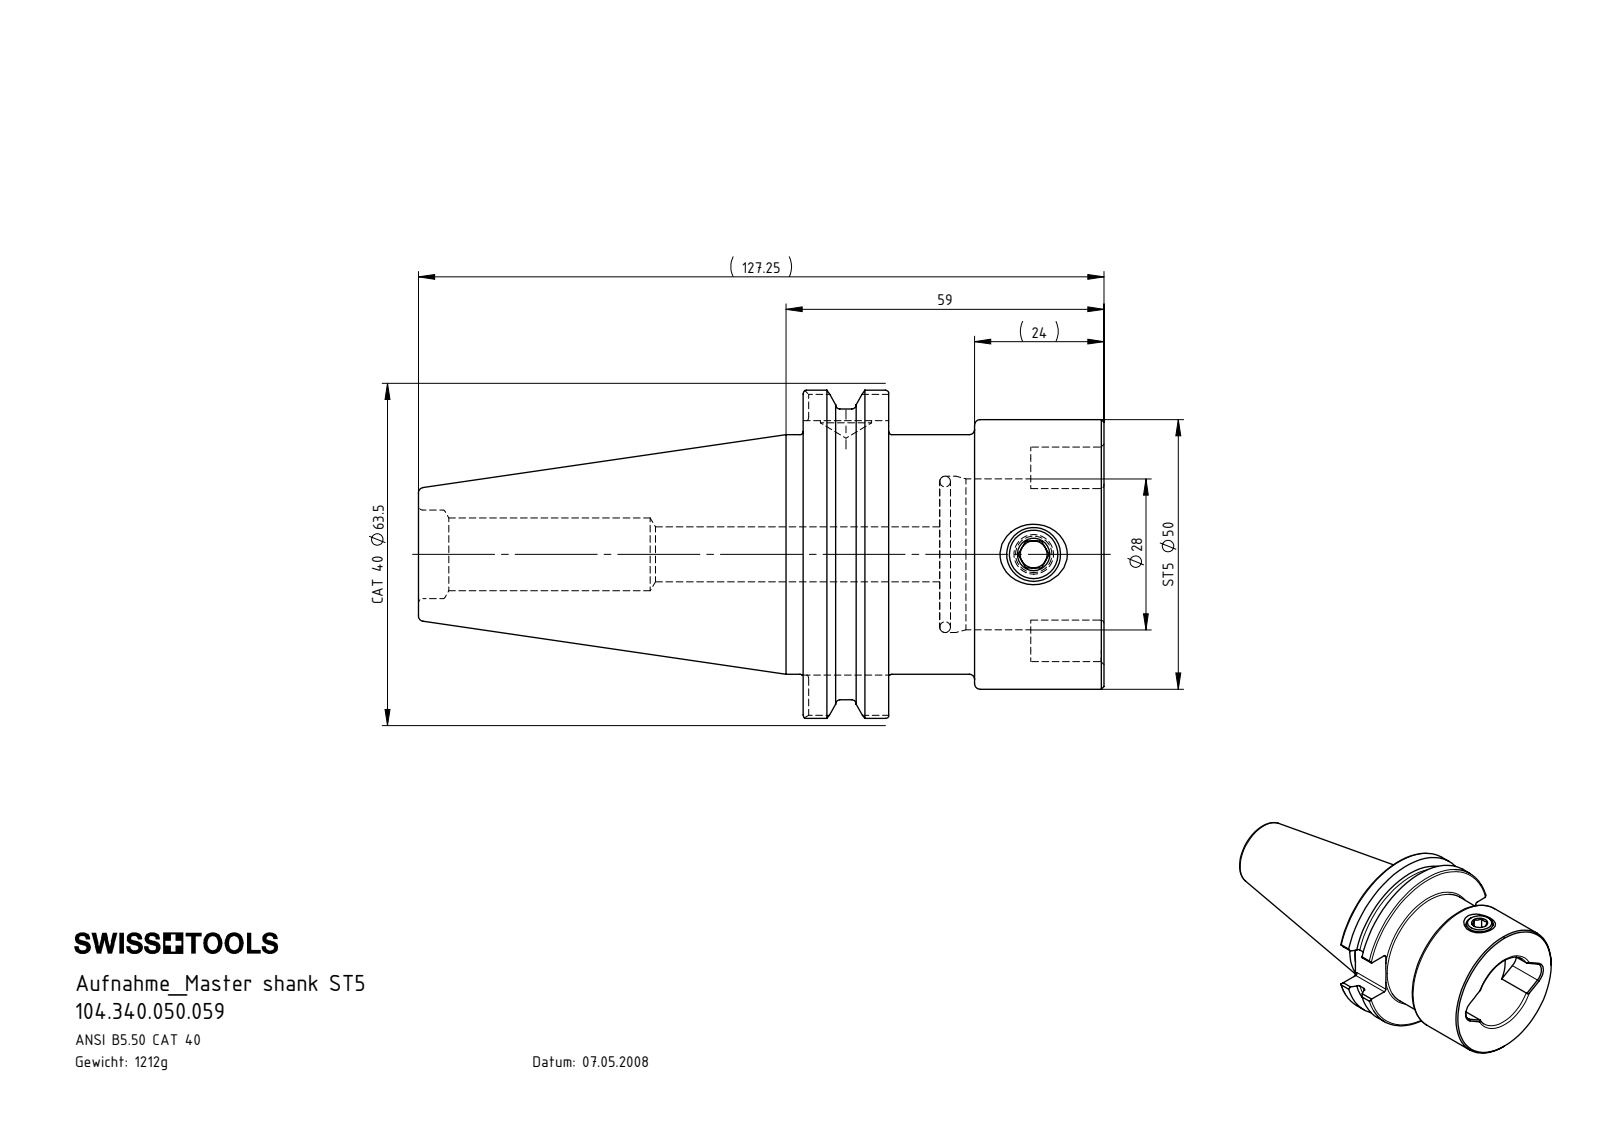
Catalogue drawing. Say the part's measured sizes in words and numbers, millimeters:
The part is named "CT4-ST5.K01.059; ST5-ER1.001.012_A; DIN 3771 - 25x2; CT4-ST5.K01.059_A". Its 3-D file was written by "SolidWorks 2015 (CONFIG_CONTROL_DESIGN)". It is 3 solids with 144 faces: 44 planar, 39 cylindrical and 61 other. Overall it measures 127.25 by 63.5 by 60.87 millimeters. Its volume is 154 722 cubic millimeters and its surface area 30 737 square millimeters. Round holes: 1 of diameter 9, 1 of diameter 9.5, 1 of diameter 10.2, 1 of diameter 13.5, 1 of diameter 16.43, 1 of diameter 28, 1 of diameter 29. Round bosses or shafts: 1 of diameter 63.5, 1 of diameter 56.36, 1 of diameter 50, 1 of diameter 44.45, 1 of diameter 10. Partial cylindrical surfaces (rounded edges, fillets, slot ends): 8 of radius 0.8, 2 of radius 4.2. The main face-to-face distances are 15.87, 55.82, 39.95, 25.32, 9.45, 30.5, 24.1, 47.2, 71.43, 87.3.
